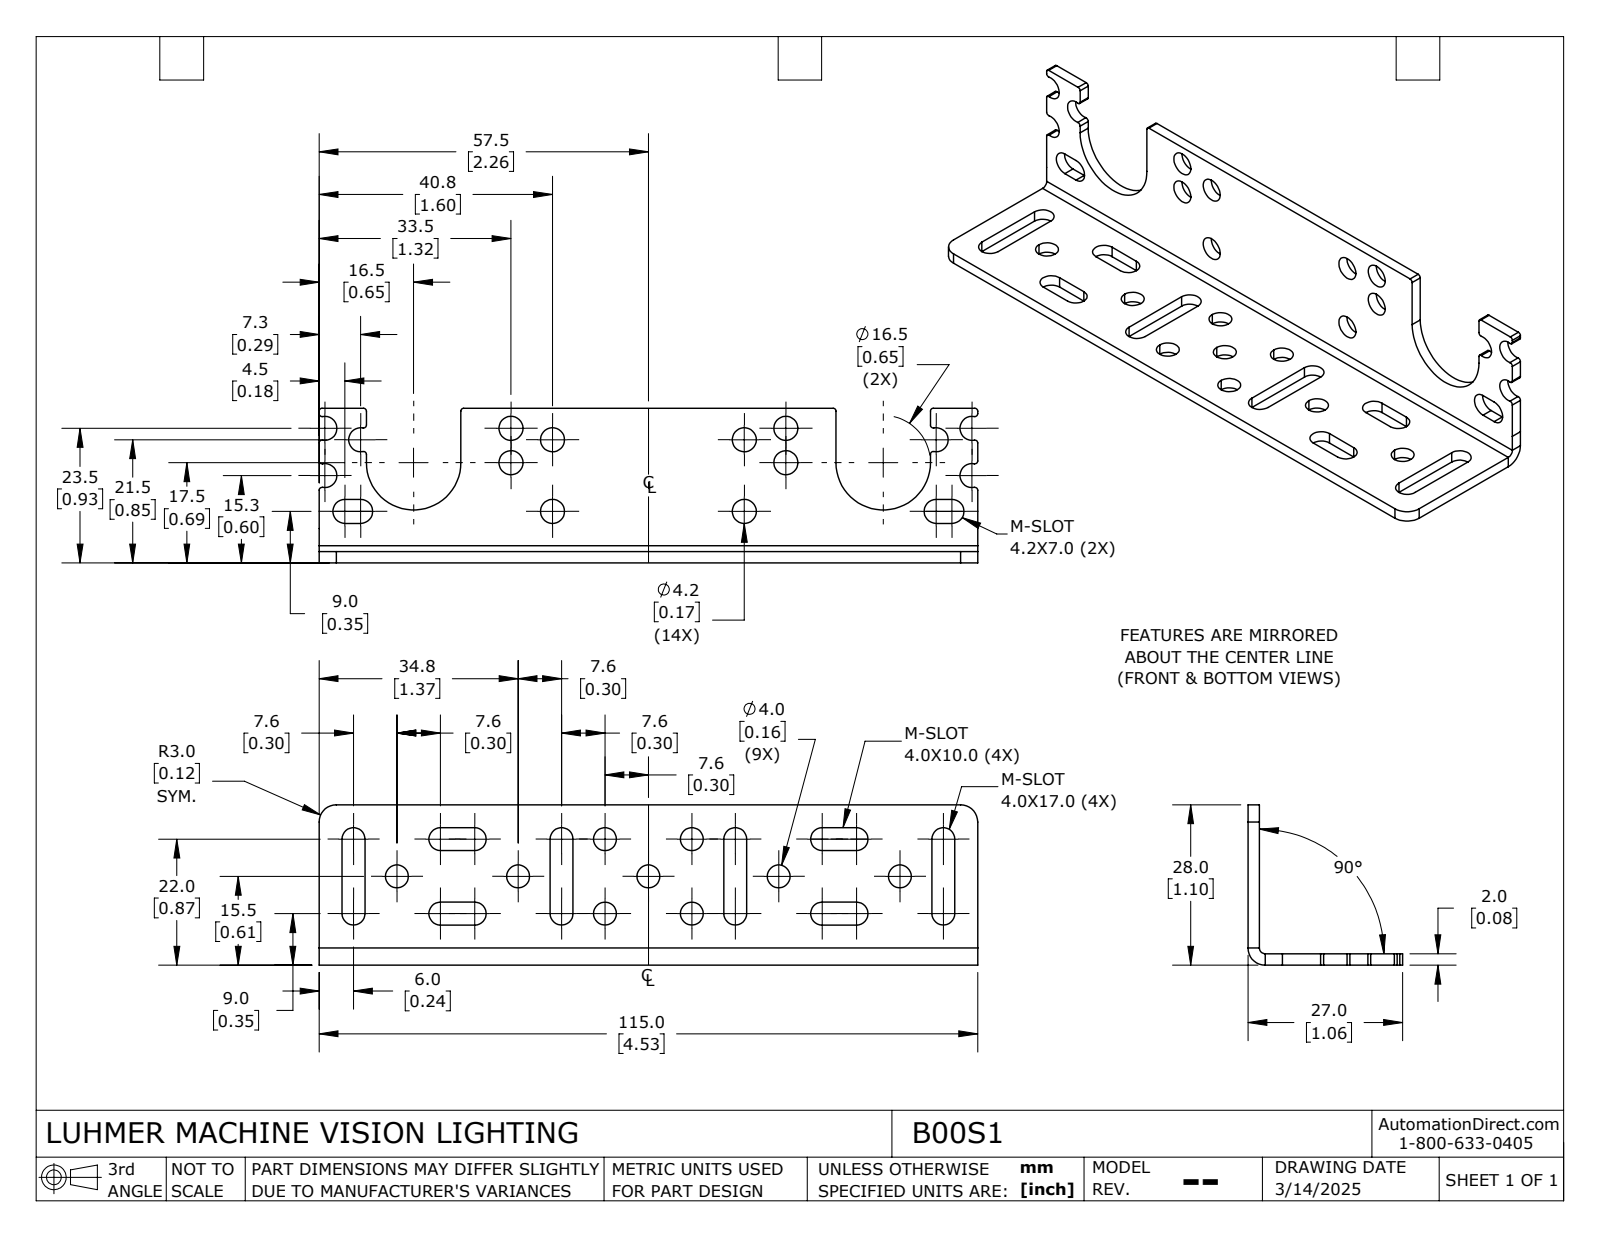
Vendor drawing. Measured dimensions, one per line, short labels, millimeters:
name: B00S1
written by: SolidWorks 2024 (AUTOMOTIVE_DESIGN)
unit: mm
bodies: 1 solid, 113 faces (46 planar, 67 cylindrical, 0 other)
size: 115 × 28 × 27
volume: 9 437 mm³; area: 11 278 mm²
holes: 9× ⌀4, 8× ⌀4.2
rounds: 18× R0.5, 16× R2, 10× R2.1, 3× R3, 2× R8.25, 1× R1
face distances: 2, 4, 28, 26, 27, 25, 40.33, 70.67, 36.33, 66.67
hole spacings: 9.99, 16.5, 31.02, 36.92, 51.91, 6, 7.52, 8.28
